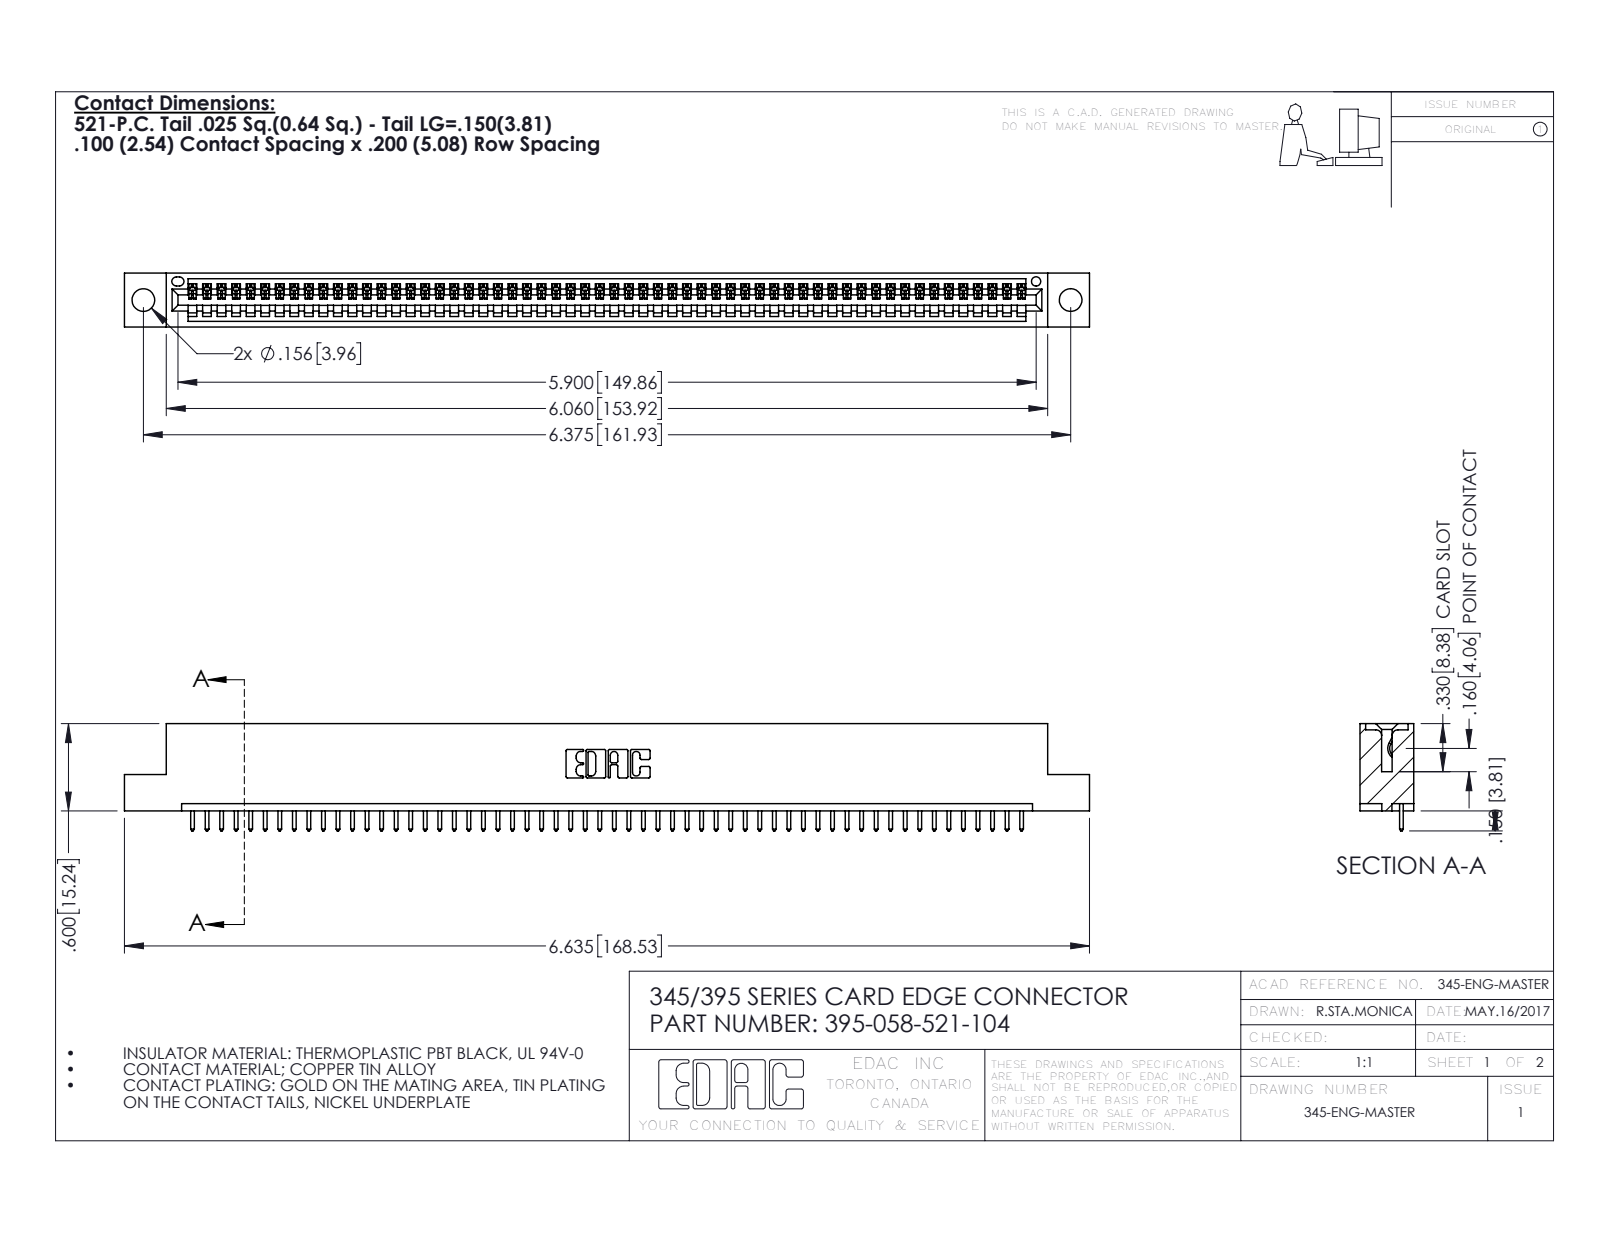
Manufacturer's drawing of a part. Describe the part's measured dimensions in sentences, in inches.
The part is named "345-292-001_345-293-121; 345 Part_Flush Mounting Lugs - 0.156 Dia-TH; 395-058-521-104". Its 3-D file was written by "SolidWorks 2016 (CONFIG_CONTROL_DESIGN)". It is 59 solids with 3490 faces: 2400 planar, 1090 cylindrical and 0 other. Overall it measures 6.635 by 0.737 by 0.37 inches. Its volume is 0.969 cubic inches and its surface area 31.76 square inches. Round holes: 2 of diameter 0.156, 1 of diameter 0.064. Partial cylindrical surfaces (rounded edges, fillets, slot ends): 116 of radius 0.006, 116 of radius 0.01, 22 of radius 0.01, 6 of radius 0.007, 6 of radius 0.031, 3 of radius 0.026, 2 of radius 0.031, 2 of radius 0.04. The main face-to-face distances are 0.298, 0.072, 0.37, 0.2, 0.098, 0.272, 0.025, 0.225, 0.149, 0.072. The hole center spacings are 0.27, 6.139, 6.375.
